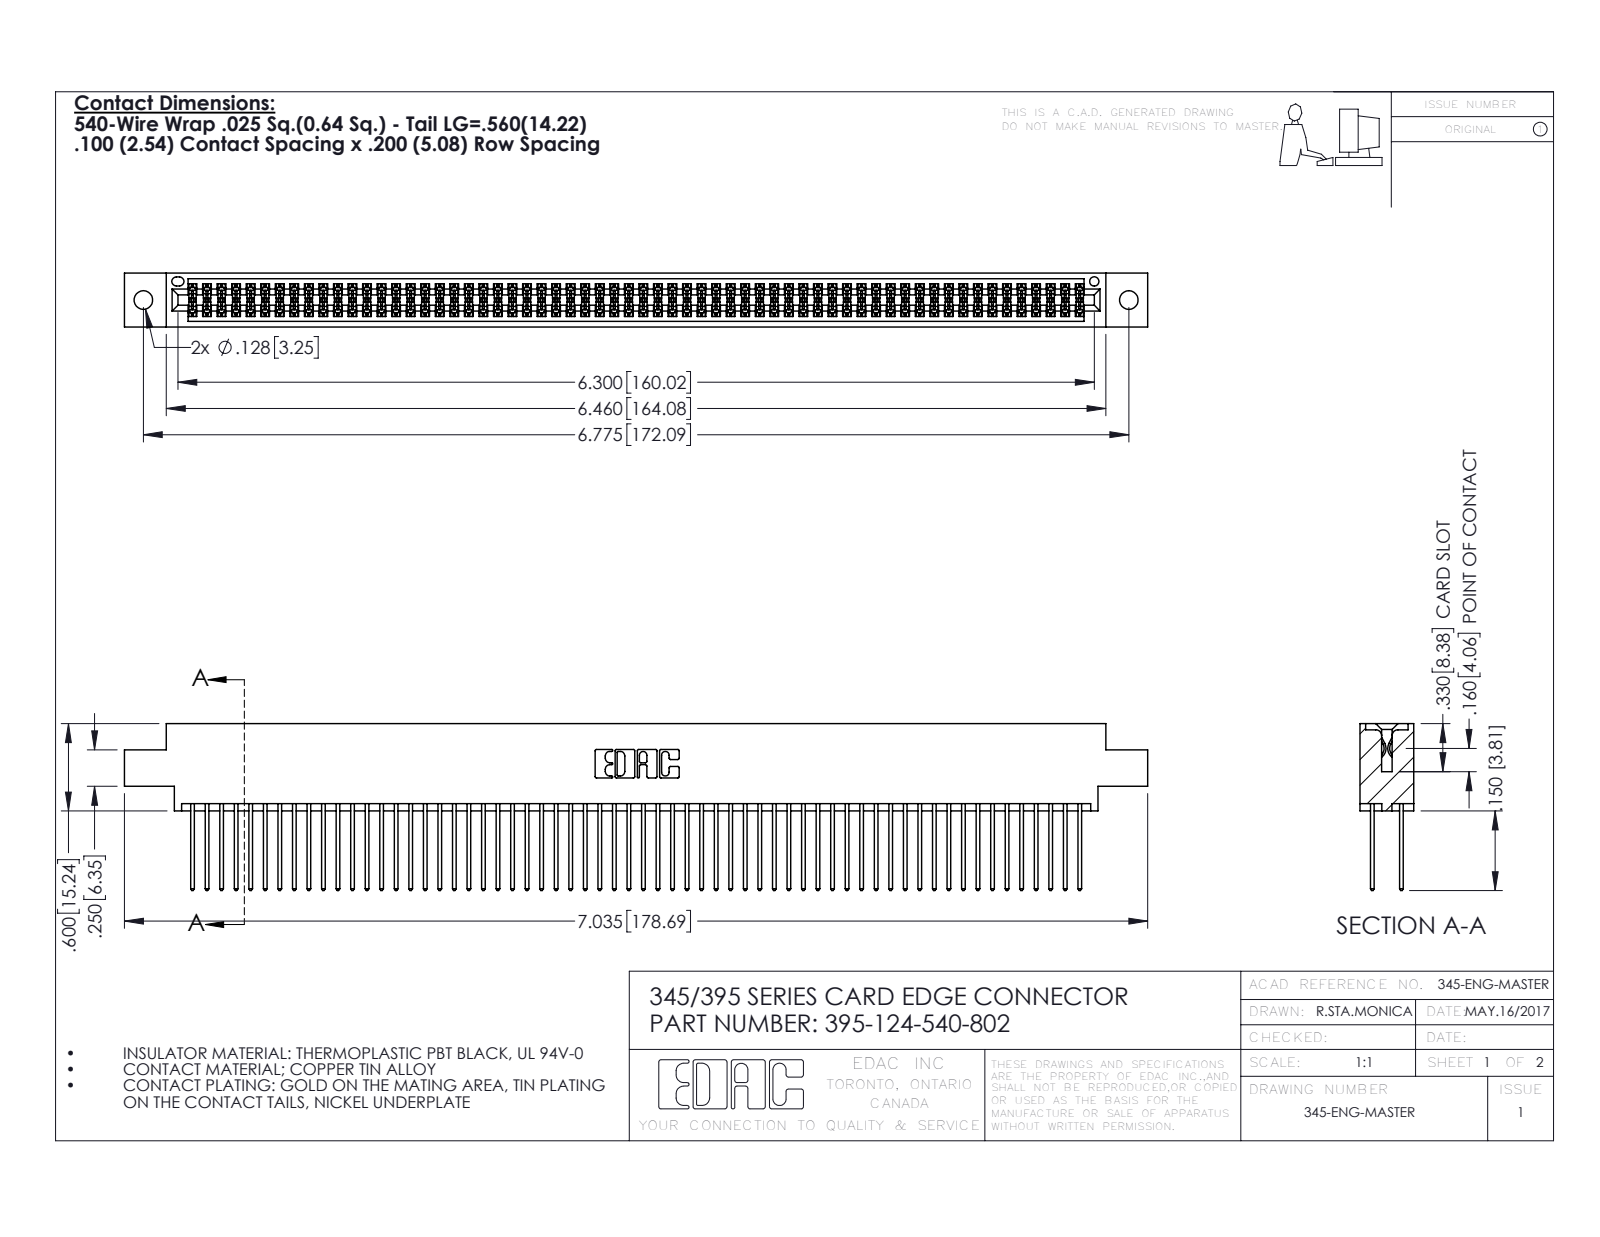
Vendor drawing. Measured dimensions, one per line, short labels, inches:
name: 345 Part_0.170 Offset - 0.128 Dia; 395-124-540-802; 345-292-001_345-293-140
written by: SolidWorks 2016 (CONFIG_CONTROL_DESIGN)
unit: in
bodies: 125 solids, 6330 faces (4176 planar, 2154 cylindrical, 0 other)
size: 7.035 × 1.147 × 0.37
volume: 1.09 in³; area: 44.71 in²
holes: 2× ⌀0.128, 1× ⌀0.064
rounds: 186× R0.006, 124× R0.01, 22× R0.01, 6× R0.007, 6× R0.031, 3× R0.026, 2× R0.014, 2× R0.019
face distances: 0.072, 0.298, 0.2, 0.098, 0.272, 0.025, 0.37, 0.225, 0.175, 0.149
hole spacings: 0.27, 6.539, 6.775
